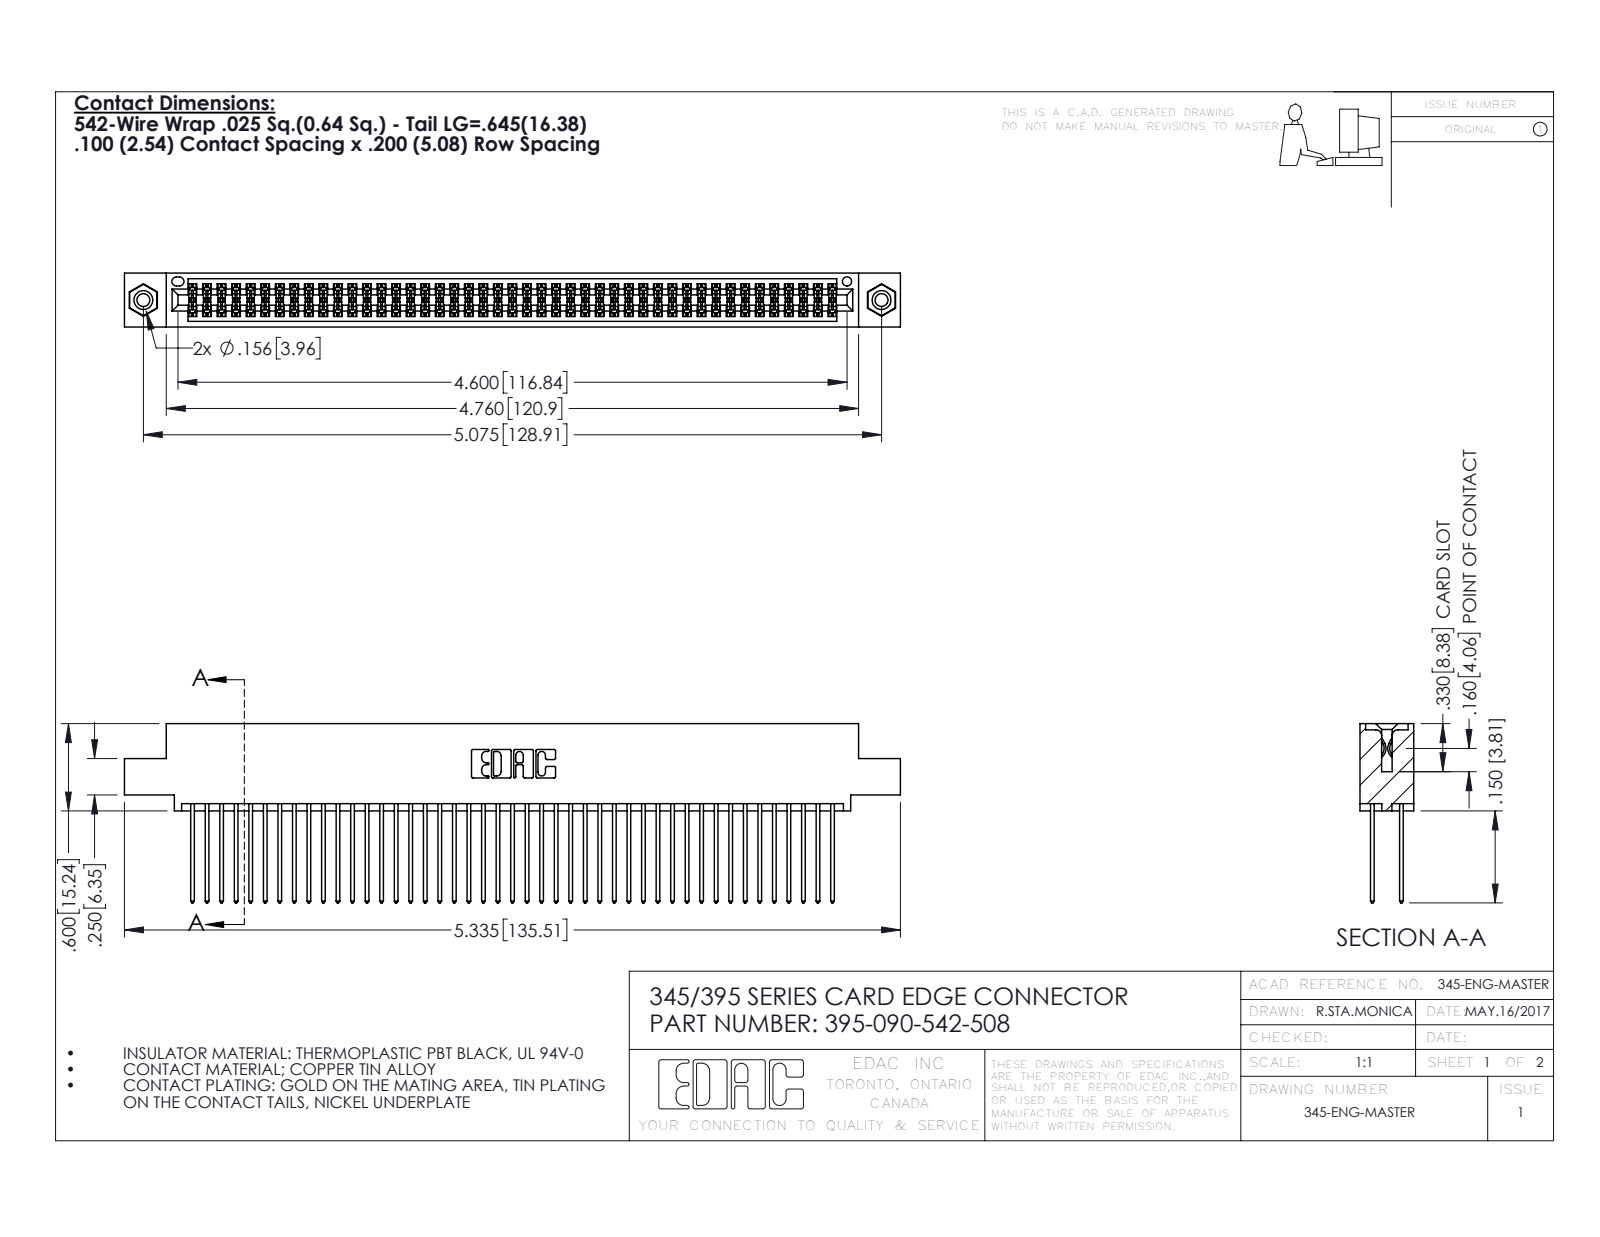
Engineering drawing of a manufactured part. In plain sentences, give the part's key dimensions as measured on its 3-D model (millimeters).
The part is named "345-250-001_345-250-003-102; 345-292-001_345-293-142; 345 Part_0.110 Offset - 0.156 Dia-TI; 395-090-542-508". Its 3-D file was written by "SolidWorks 2016 (CONFIG_CONTROL_DESIGN)". It is 93 solids with 4690 faces: 3086 planar, 1588 cylindrical and 16 other. Overall it measures 135.5 by 31.3 by 9.4 millimeters. Its volume is 13 500 cubic millimeters and its surface area 22 130 square millimeters. Round holes: 2 of diameter 2.3, 2 of diameter 3.2, 2 of diameter 4, 1 of diameter 1.6. Round bosses or shafts: 2 of diameter 3.9. Partial cylindrical surfaces (rounded edges, fillets, slot ends): 135 of radius 0.2, 90 of radius 0.3, 22 of radius 0.3, 6 of radius 0.2, 6 of radius 0.8, 3 of radius 0.7, 2 of radius 0.4, 2 of radius 0.5. The main face-to-face distances are 1.8, 7.6, 5.1, 2.5, 6.9, 0.6, 5.7, 9.4, 4.4, 3.8. The hole center spacings are 6.9, 122.9, 128.9.
